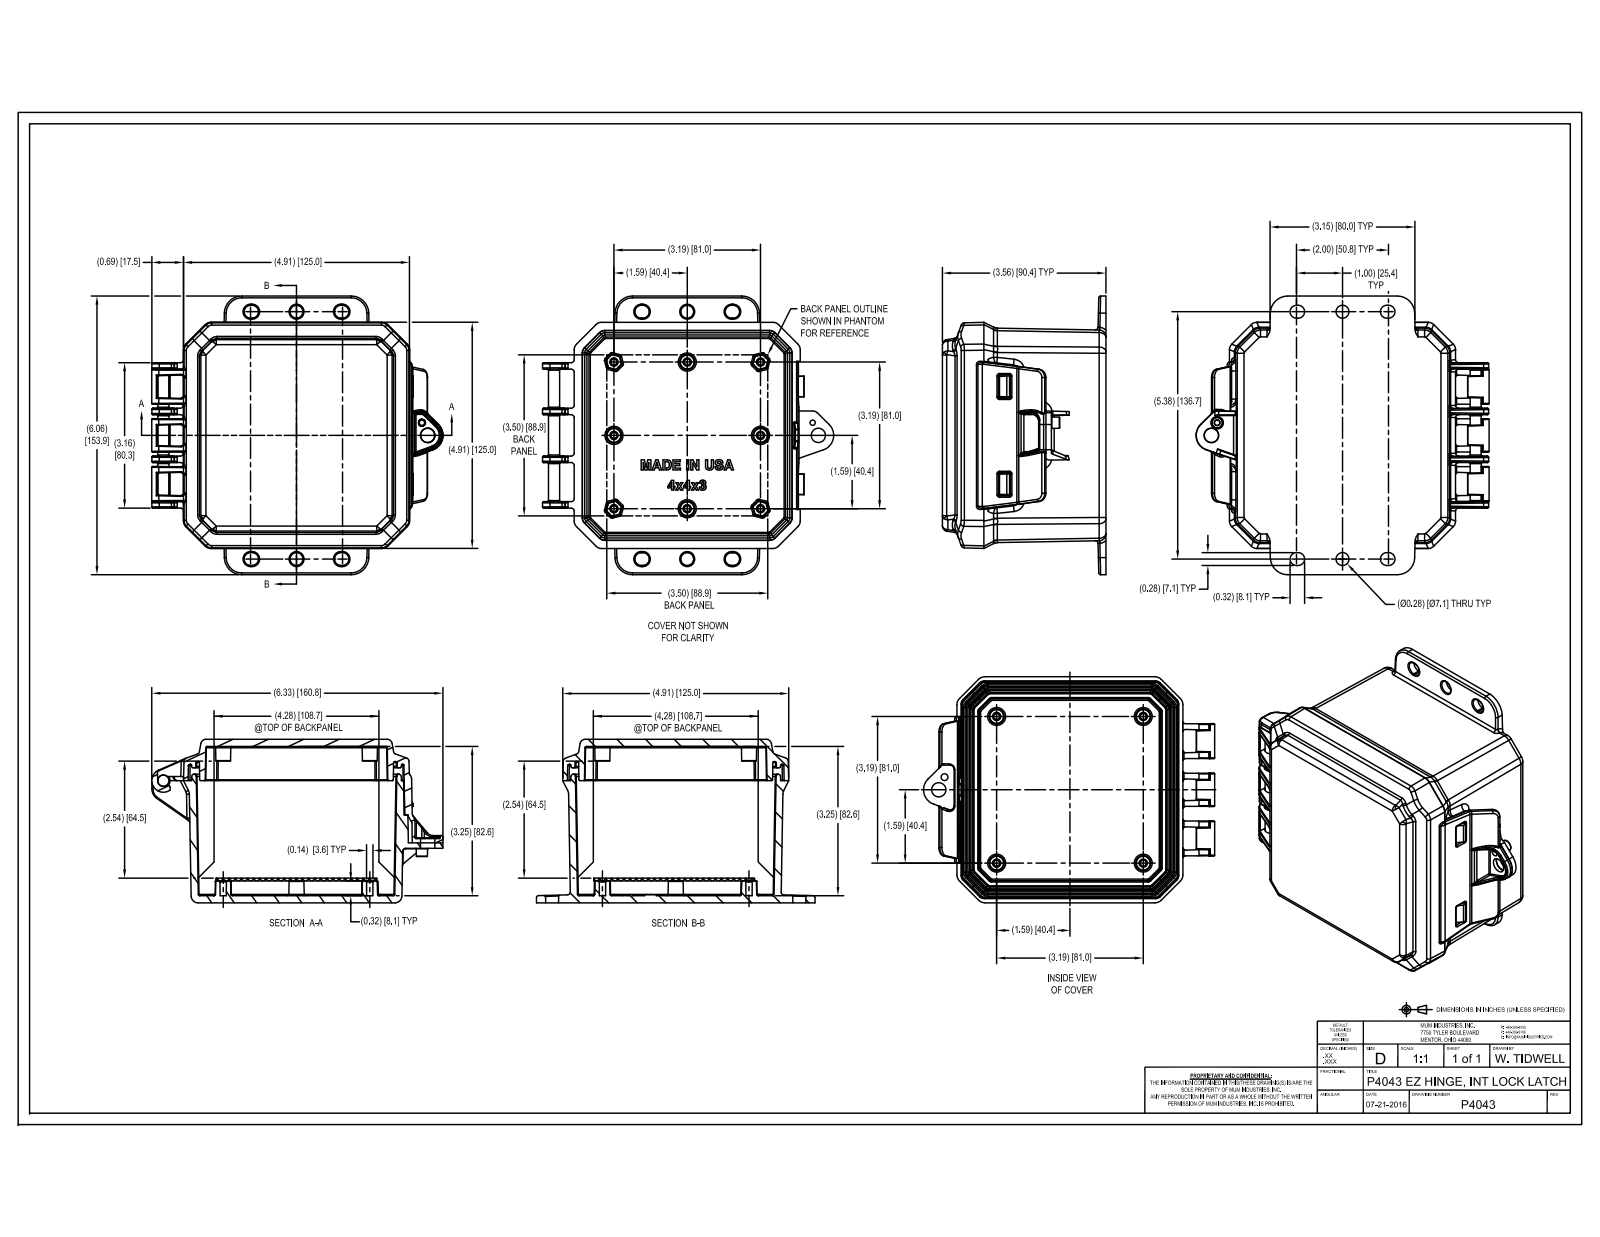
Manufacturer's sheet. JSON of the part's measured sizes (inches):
{"part_name": "P443BH; P44CHO; P4043_ASM", "step_written_by": "CREO PARAMETRIC BY PTC INC, 2016050 (CONFIG_CONTROL_DESIGN)", "units": "inches", "bodies": {"solids": 2, "faces": 1808, "planar": 510, "cylindrical": 601, "other": 697}, "overall_size": [6.331, 6.056, 3.555], "volume_in3": 18.42, "surface_area_in2": 257.8, "round_bosses_or_shafts": [[0.242, 1]], "partial_cylinders_radius": [[0.025, 85], [0.03, 77], [0.02, 52], [0.01, 51], [0.06, 45], [0.19, 32], [0.015, 29], [0.062, 17]], "face_to_face_distances": [0.155, 3.4, 3.555, 3.245, 4.32, 4.165, 0.9, 2.655, 2.5, 0.745]}
